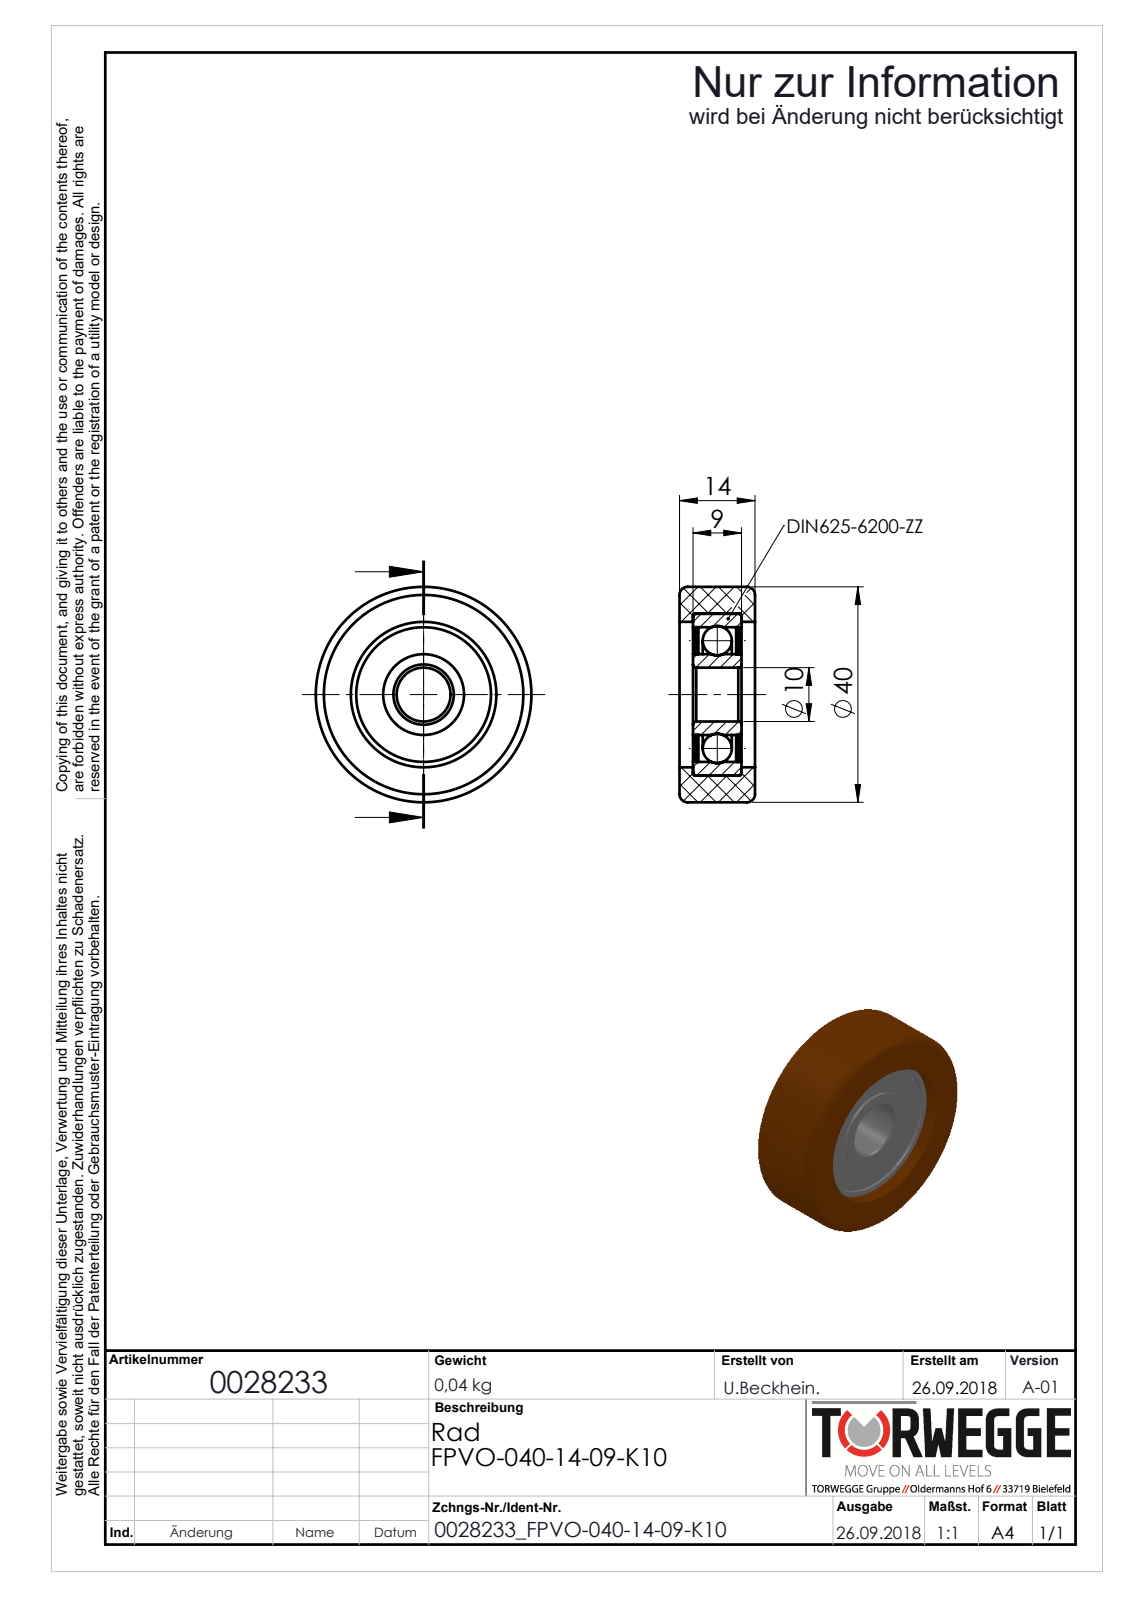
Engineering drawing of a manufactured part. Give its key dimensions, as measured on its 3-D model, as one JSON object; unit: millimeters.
{"part_name": "0028233_FPVO-040-14-09-K10", "step_written_by": "SolidWorks 2018 (AUTOMOTIVE_DESIGN)", "units": "millimeters", "bodies": {"solids": 6, "faces": 66, "planar": 12, "cylindrical": 28, "other": 26}, "overall_size": [40, 40, 14], "volume_mm3": 12765, "surface_area_mm2": 9763, "round_holes": [[10, 1], [15, 1], [25, 1], [27, 1], [30, 1]], "round_bosses_or_shafts": [[40, 1]], "face_to_face_distances": [0.5, 8, 2.5, 11.5, 3, 3.5, 10.5, 11, 1, 8.5]}
